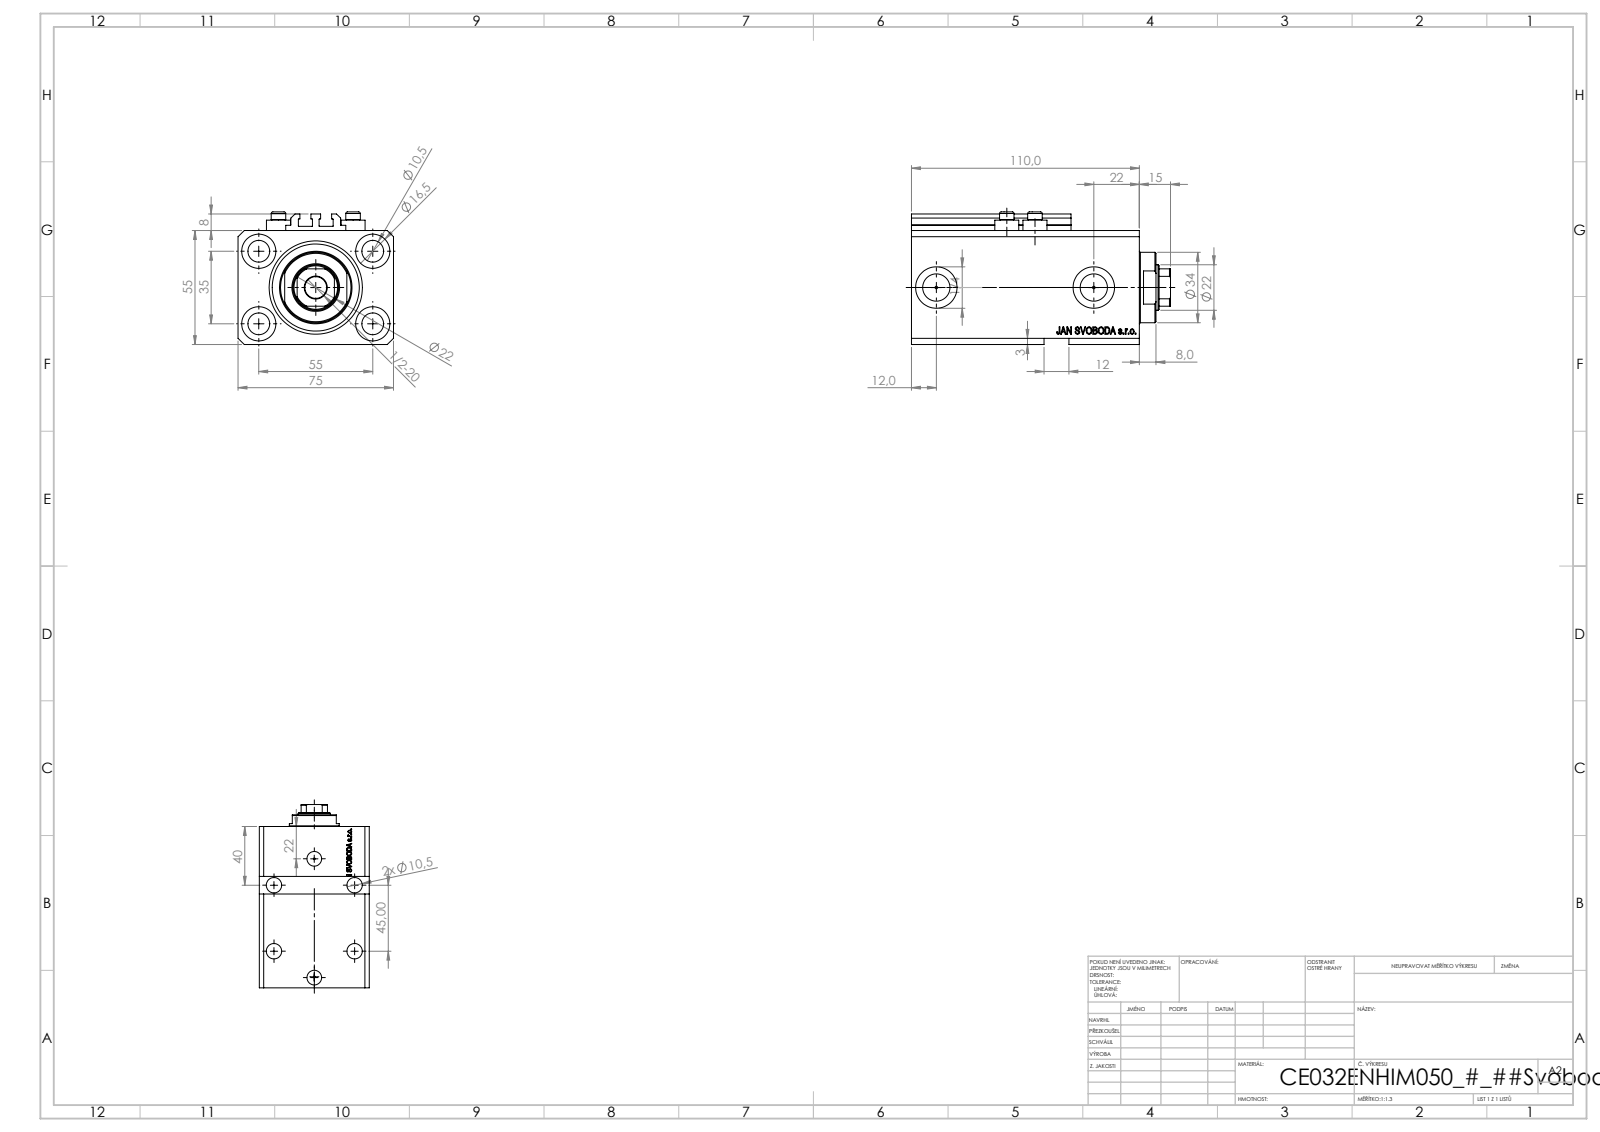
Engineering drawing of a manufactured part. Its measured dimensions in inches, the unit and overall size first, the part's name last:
Units: inches
Overall size (bounding box): 4.921 × 2.953 × 2.52
Round holes (diameter × count): ⌀0.413 ×9, ⌀0.049 ×4, ⌀0.157 ×4, ⌀0.65 ×4, ⌀0.394 ×2, ⌀0.518 ×2, ⌀0.787 ×2, ⌀0.866 ×1, ⌀1.26 ×1, ⌀1.772 ×1
Round bosses / shafts (diameter × count): ⌀0.457 ×4, ⌀0.276 ×4, ⌀1.339 ×1
Partial cylindrical surfaces — rounded edges, fillets, slot ends (radius × count): R0.008 ×10, R0.413 ×1
Main face-to-face distances: 2.165, 2.953, 0.591, 4.331, 3.74, 0.118, 0.39, 3.35, 3.941, 2.244
Hole centre spacings: 1.283, 1.294, 2.165, 2.706, 0.535, 0.555, 0.907, 1.016
Volume: 23.27 in³ · Surface area: 148.2 in²
Bodies: 8 solids, 1084 faces (514 planar, 146 cylindrical, 424 other)
Part name (STEP PRODUCT): V250CE_E_Body; ALLEN BOLT V250CE; V250CE_VC_E; V250CE_C_VCP
STEP written by: SolidWorks 2019 (CONFIG_CONTROL_DESIGN)
